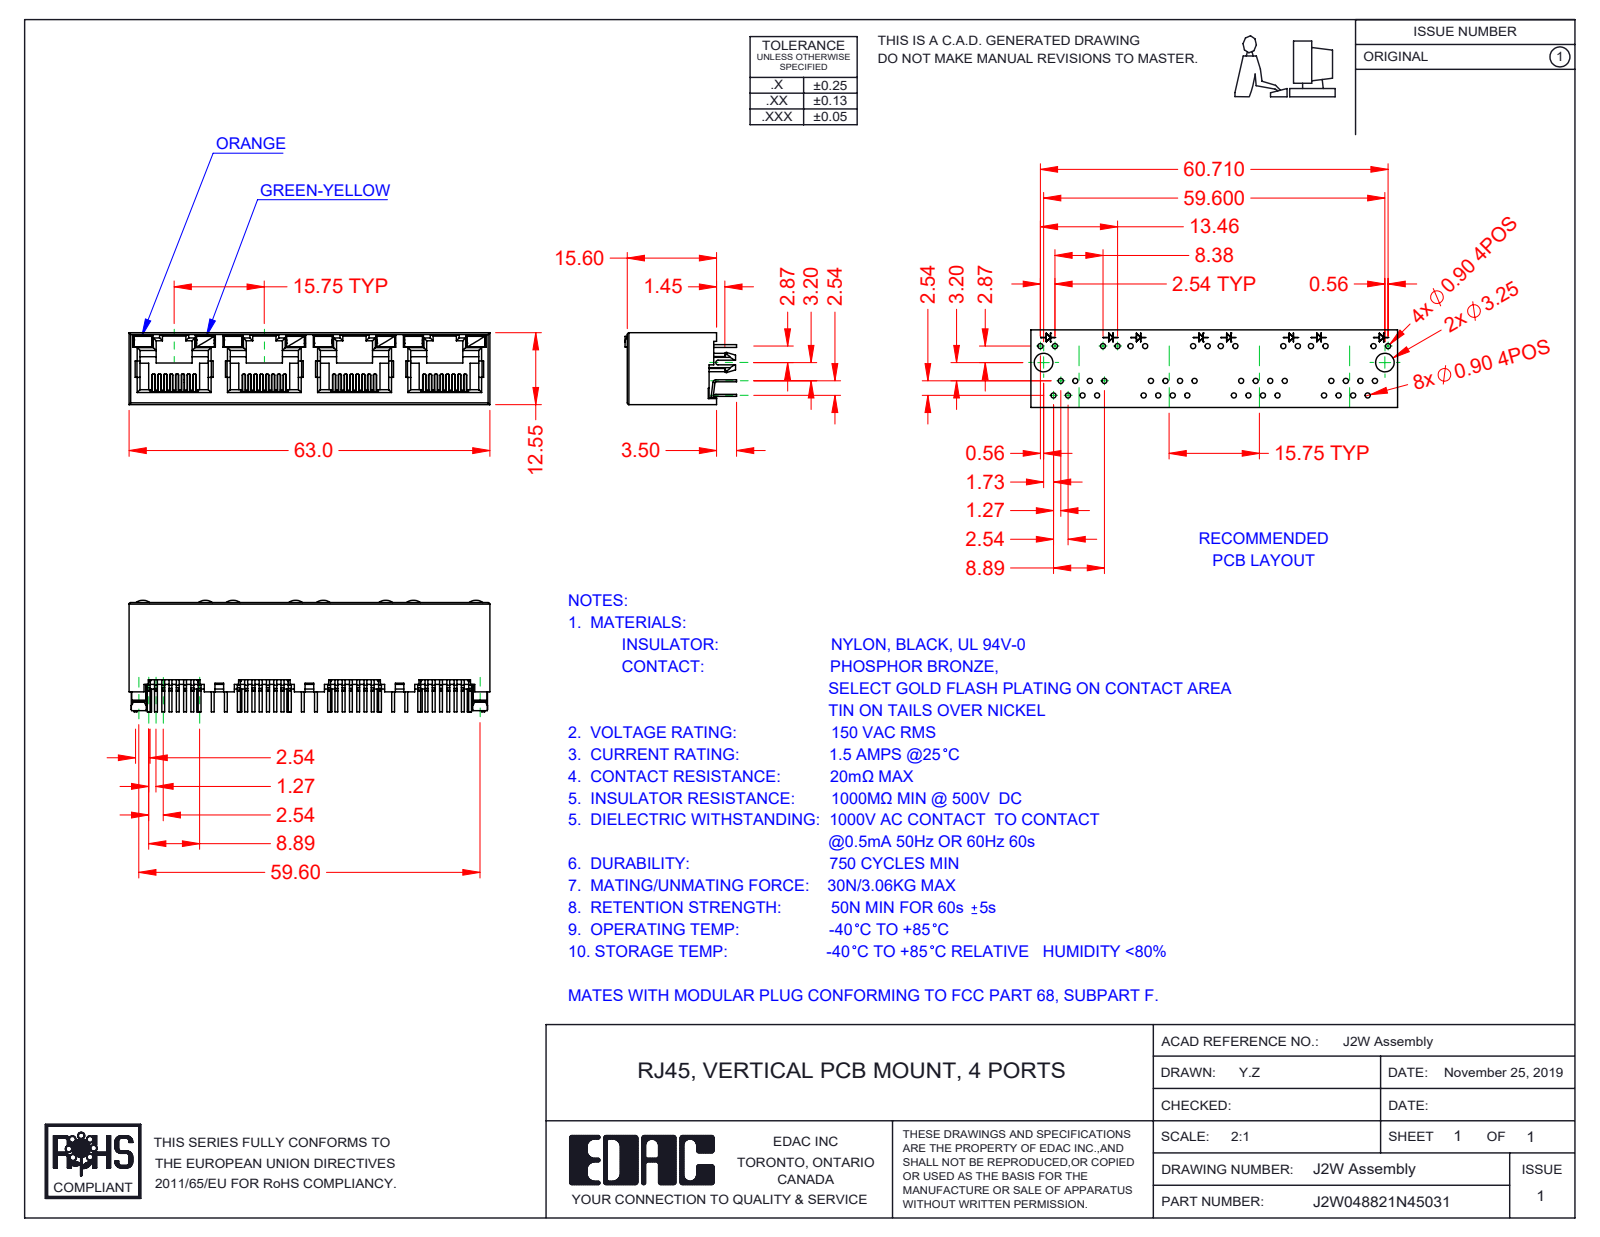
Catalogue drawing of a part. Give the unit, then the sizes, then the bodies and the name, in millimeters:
Units: millimetres
Overall size (bounding box): 63 × 19.5 × 12.55
Partial cylindrical surfaces — rounded edges, fillets, slot ends (radius × count): R0.15 ×64, R0.2 ×29, R0.5 ×28, R0.3 ×14, R0.45 ×8, R2 ×8, R0.25 ×2, R1.5 ×2
Main face-to-face distances: 12.55, 11.9, 0.65, 15.75, 0.36, 1.5, 0.78, 0.6, 11.3, 31.5
Volume: 5 335 mm³ · Surface area: 13 144 mm²
Bodies: 45 solids, 3139 faces (2600 planar, 481 cylindrical, 58 other)
Part name (STEP PRODUCT): 2W LED RH_5-Green-Yellow; 2W Insulator; 2W Contact Lock; 2W LED LH_4-Orange (+2 more)
STEP written by: SolidWorks 2020 (CONFIG_CONTROL_DESIGN)
